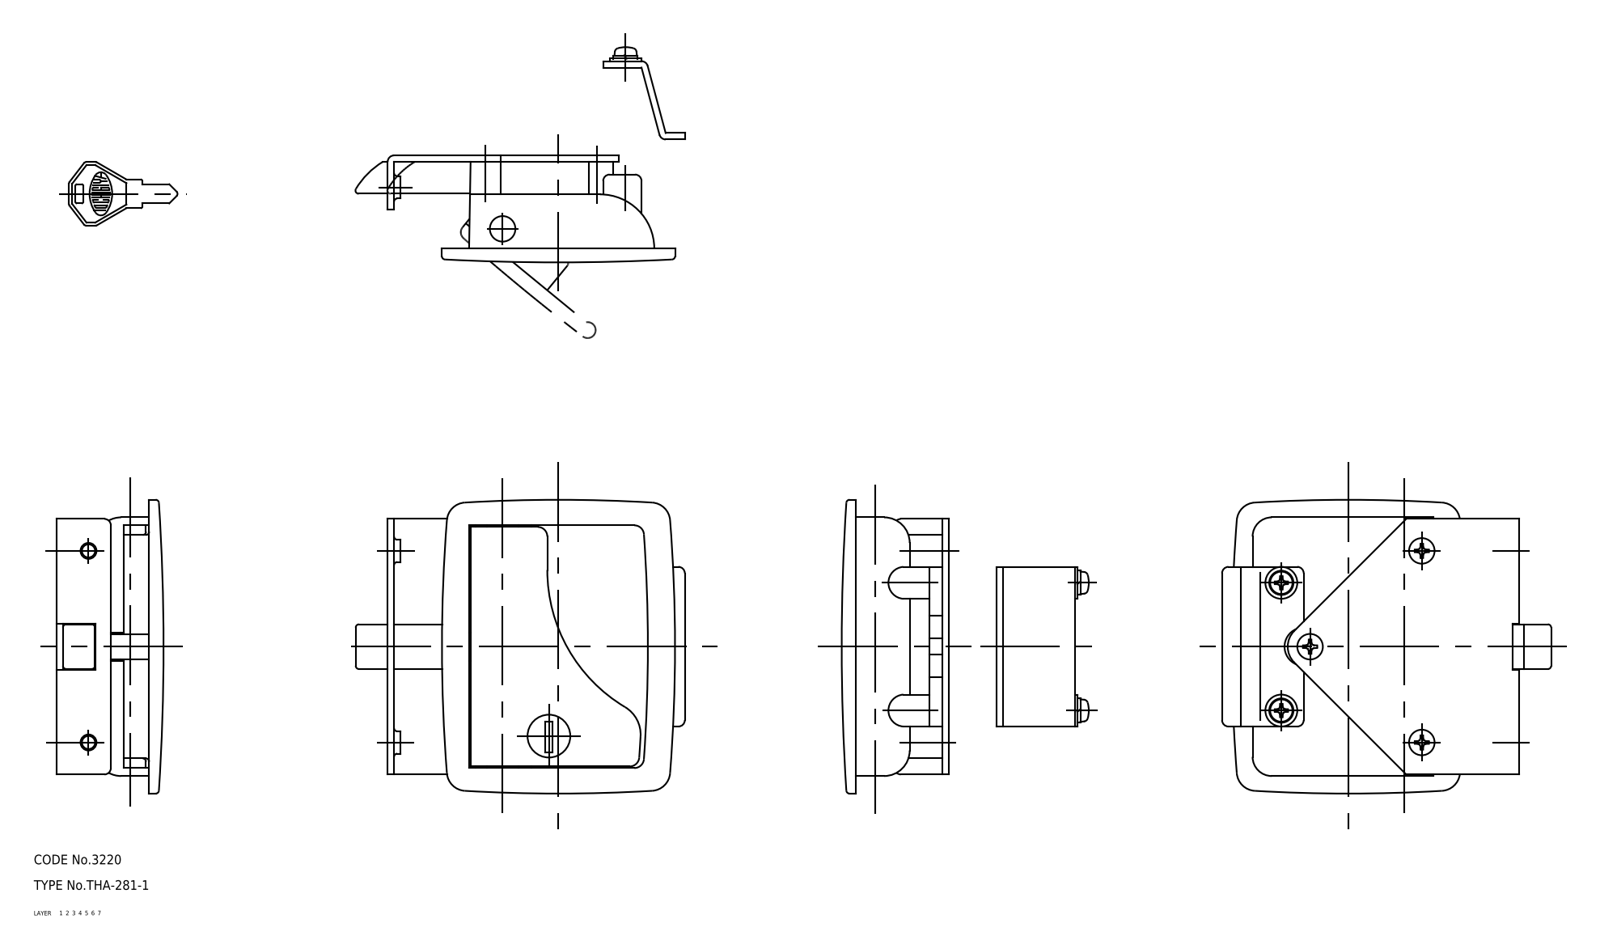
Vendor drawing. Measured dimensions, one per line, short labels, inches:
name: bracket_B; screw; lock; handle (+5 more)
written by: CADfix (AUTOMOTIVE_DESIGN)
unit: in
bodies: 9 solids, 505 faces (0 planar, 0 cylindrical, 505 other)
size: 4.072 × 3.842 × 3.622
volume: 4.367 in³; area: 88.76 in²
